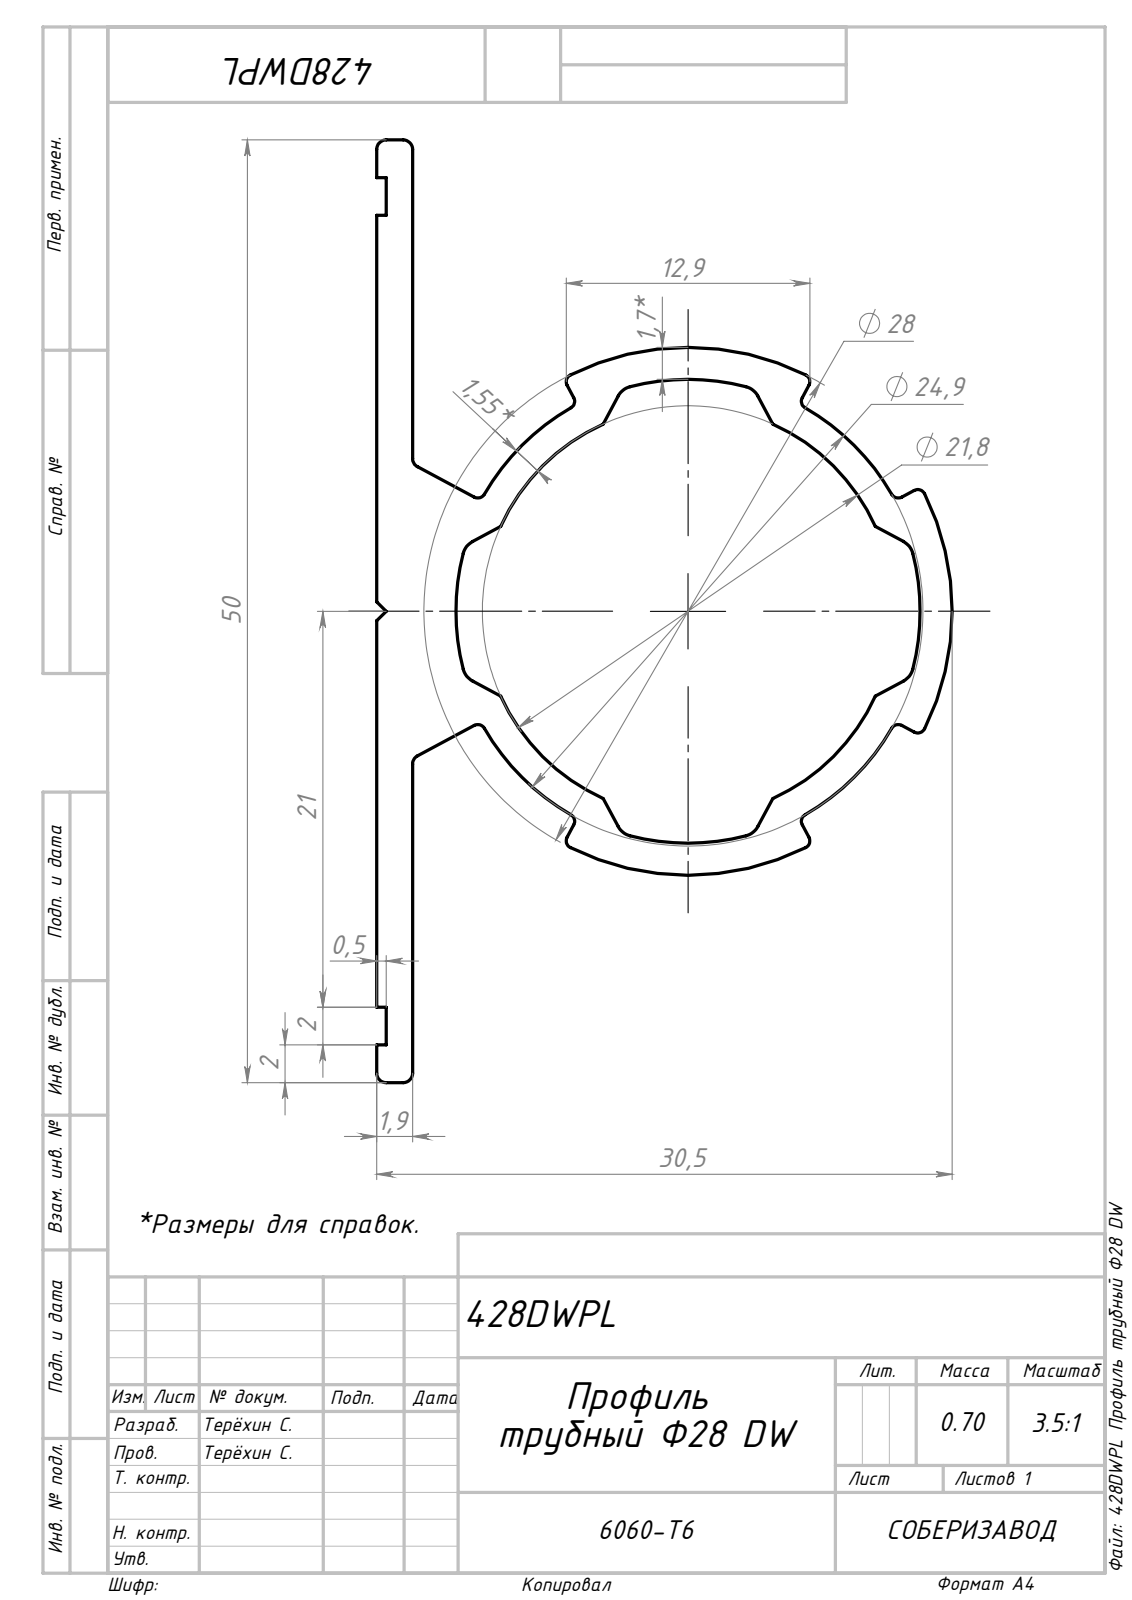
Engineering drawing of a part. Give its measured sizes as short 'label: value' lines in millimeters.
name: 428DWPL Профиль трубный Φ28 DW
written by: SolidWorks 2022 (AUTOMOTIVE_DESIGN)
unit: mm
bodies: 1 solid, 82 faces (34 planar, 48 cylindrical, 0 other)
size: 1000 × 50 × 30.5
volume: 259 116 mm³; area: 252 148 mm²
rounds: 14× R0.4, 8× R1, 6× R0.5, 1× R10.9, 1× R12.3, 1× R12.45, 1× R14
face distances: 1.9, 17.32, 0.5, 1.4, 2, 46, 4, 48, 44, 50
